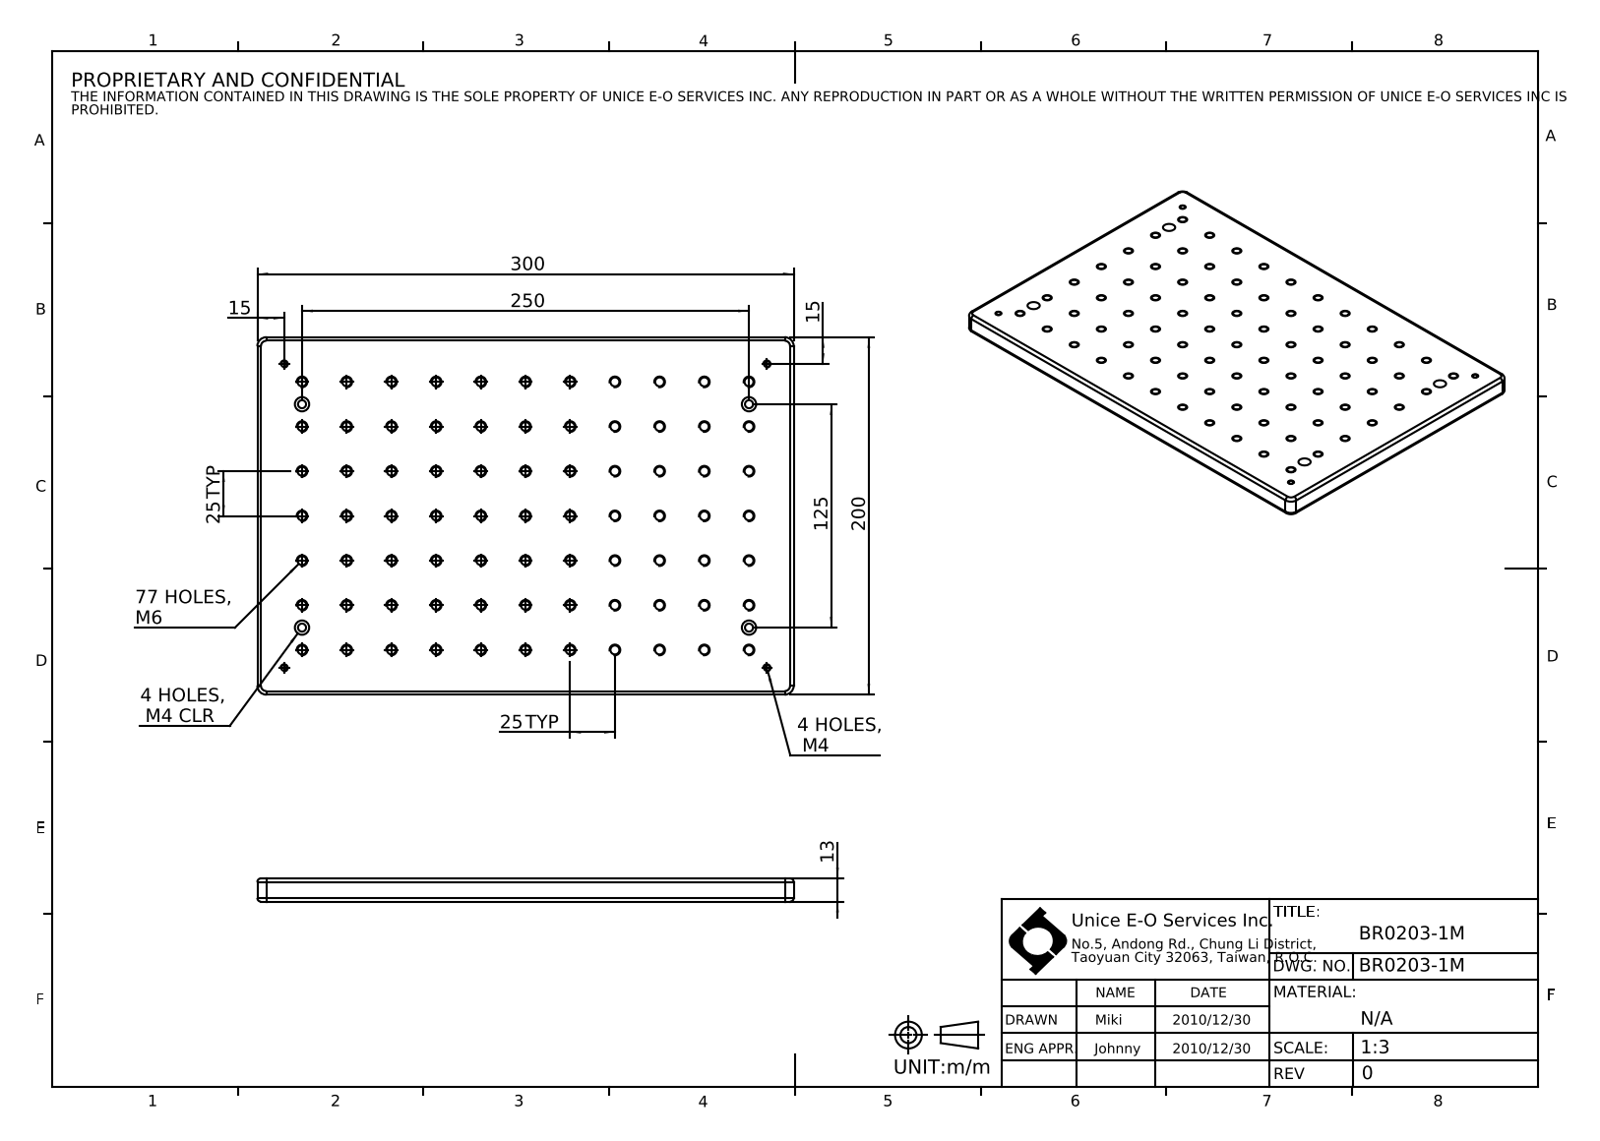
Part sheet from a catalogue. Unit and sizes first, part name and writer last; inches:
Units: inches
Overall size (bounding box): 11.811 × 7.874 × 0.512
Round holes (diameter × count): ⌀0.197 ×77, ⌀0.13 ×4, ⌀0.177 ×4, ⌀0.315 ×4
Partial cylindrical surfaces — rounded edges, fillets, slot ends (radius × count): R0.079 ×8, R0.197 ×4
Main face-to-face distances: 0.512, 7.874, 11.811, 0.276, 0.236
Hole centre spacings: 0.984, 1.969, 5.987, 2.953, 4.921, 6.225, 5.906, 6.603
Volume: 46.15 in³ · Surface area: 225 in²
Bodies: 1 solid, 208 faces (10 planar, 190 cylindrical, 8 other)
Part name (STEP PRODUCT): BR0203-1M
STEP written by: SolidWorks 2016 (CONFIG_CONTROL_DESIGN)
